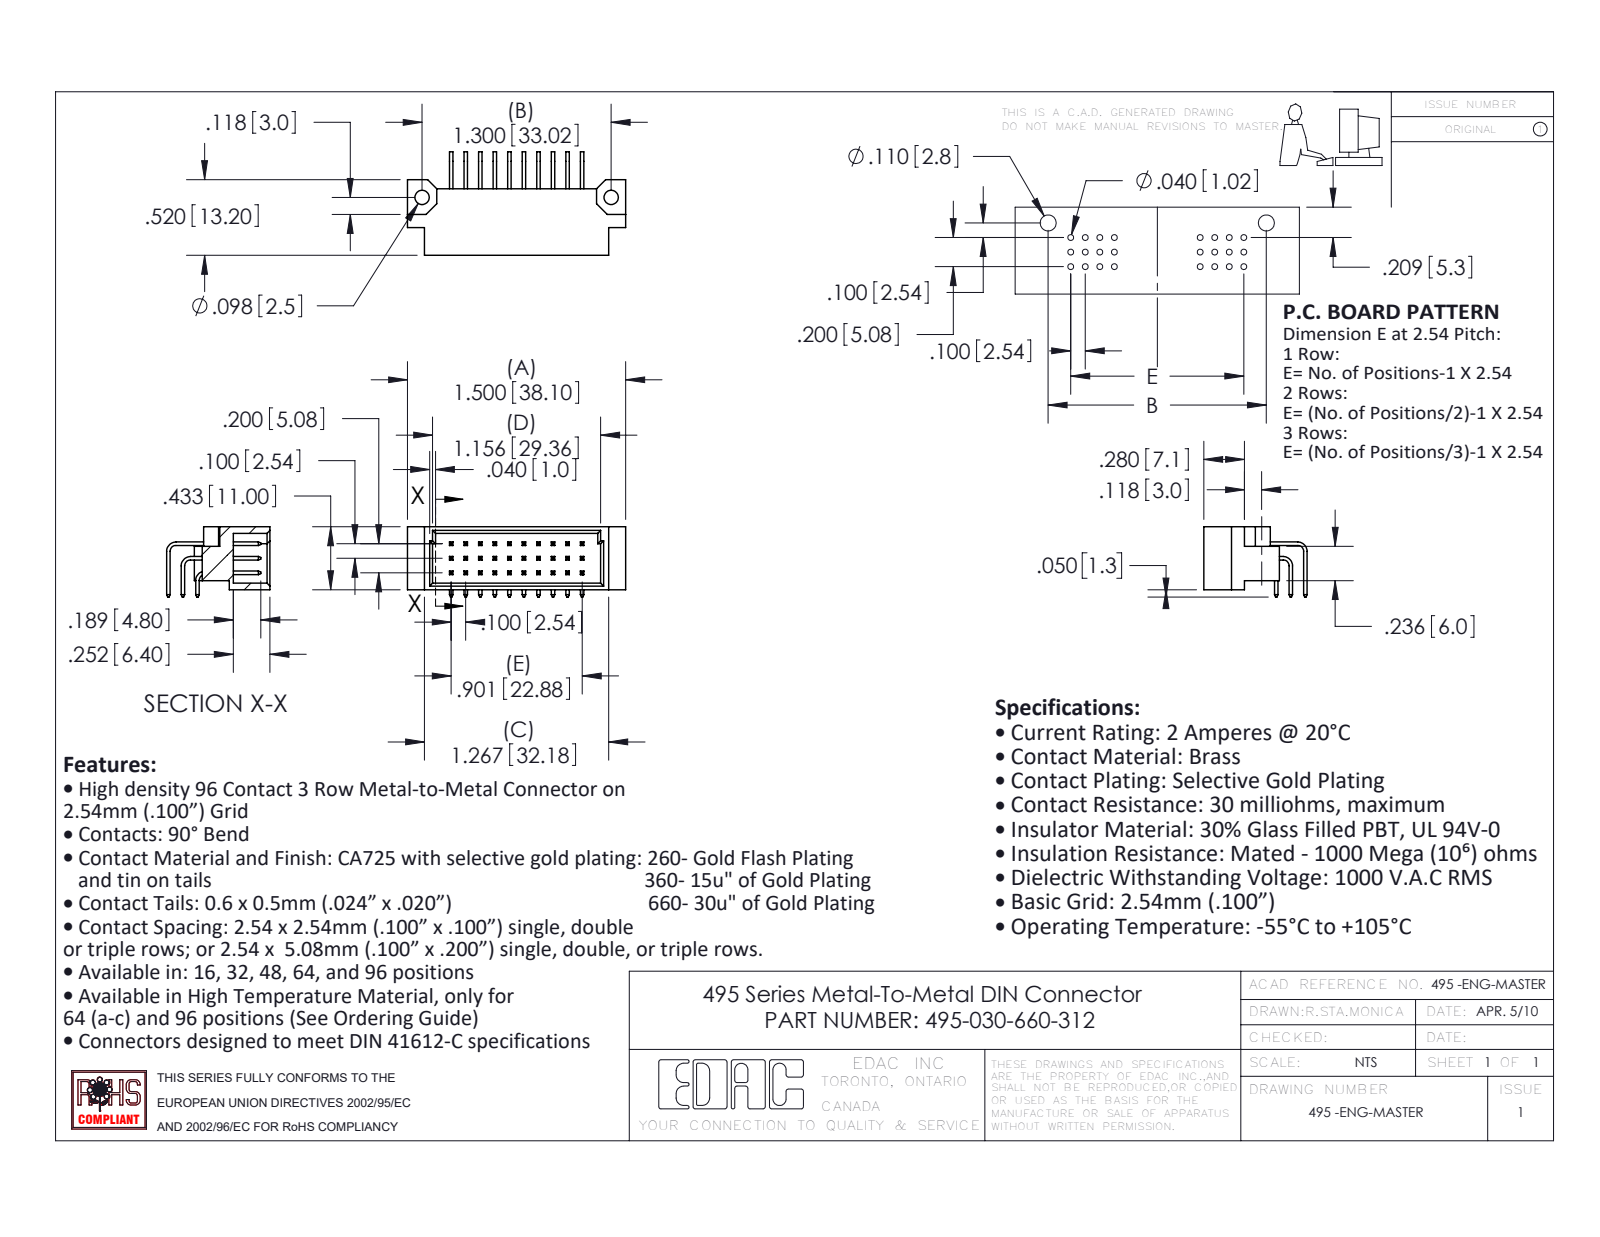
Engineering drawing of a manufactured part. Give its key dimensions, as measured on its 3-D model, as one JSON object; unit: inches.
{"part_name": "495-290-1; 495-030-660-312; 495-290-2; 495-290-3 (+1 more)", "step_written_by": "SolidWorks 2020 (AUTOMOTIVE_DESIGN)", "units": "inches", "bodies": {"solids": 31, "faces": 709, "planar": 645, "cylindrical": 64, "other": 0}, "overall_size": [1.5, 0.711, 0.483], "volume_in3": 0.163, "surface_area_in2": 6.645, "round_holes": [[0.098, 2]], "partial_cylinders_radius": [[0.04, 3], [0.065, 3]], "face_to_face_distances": [0.1, 0.2, 0.3, 0.388, 0.024, 0.4, 0.205, 0.045, 0.5, 0.024], "hole_center_spacings": [1.3]}
